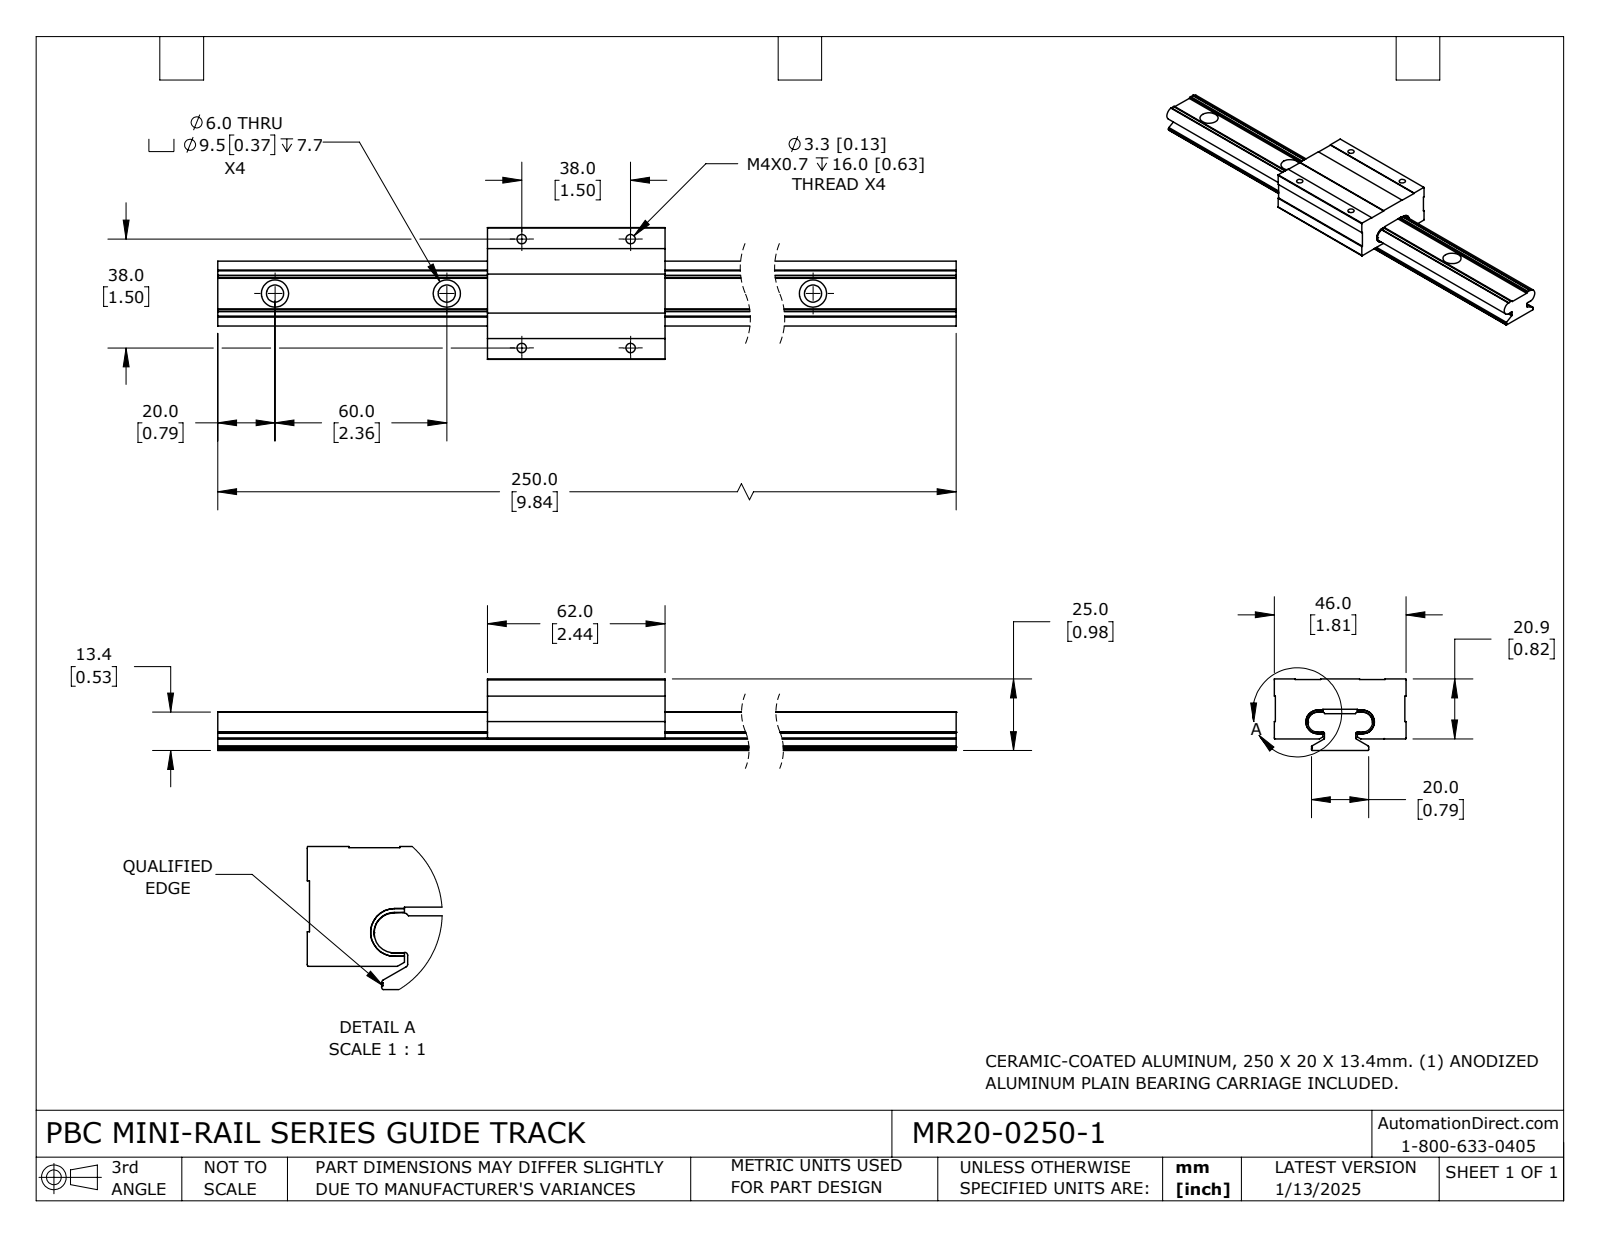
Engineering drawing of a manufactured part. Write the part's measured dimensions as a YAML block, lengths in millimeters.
part_name: "MR20-0250-1; MR20-0250-1_RAIL; MR20-0250-1_CARRIAGE"
step_written_by: "SolidWorks 2023 (CONFIG_CONTROL_DESIGN)"
units: millimeters
bodies: {solids: 4, faces: 135, planar: 81, cylindrical: 54, other: 0}
overall_size: [250, 46, 25]
volume: 103100
surface_area: 38710
round_holes:
  - {diameter: 3.3, count: 4}
  - {diameter: 6, count: 4}
  - {diameter: 9.5, count: 4}
partial_cylinders:
  - {radius: 0.5, count: 10}
  - {radius: 3.6, count: 4}
  - {radius: 1, count: 2}
  - {radius: 3.5, count: 2}
  - {radius: 3.5, count: 2}
  - {radius: 4.2, count: 2}
  - {radius: 0.1, count: 1}
face_to_face_distances: [12.9, 4.1, 8.8, 25, 20.9, 12.1, 24.8, 20.7, 11.9, 0.4]
hole_center_spacings: [60, 19.5, 32.4, 38, 38, 38.8, 53.7, 59]
